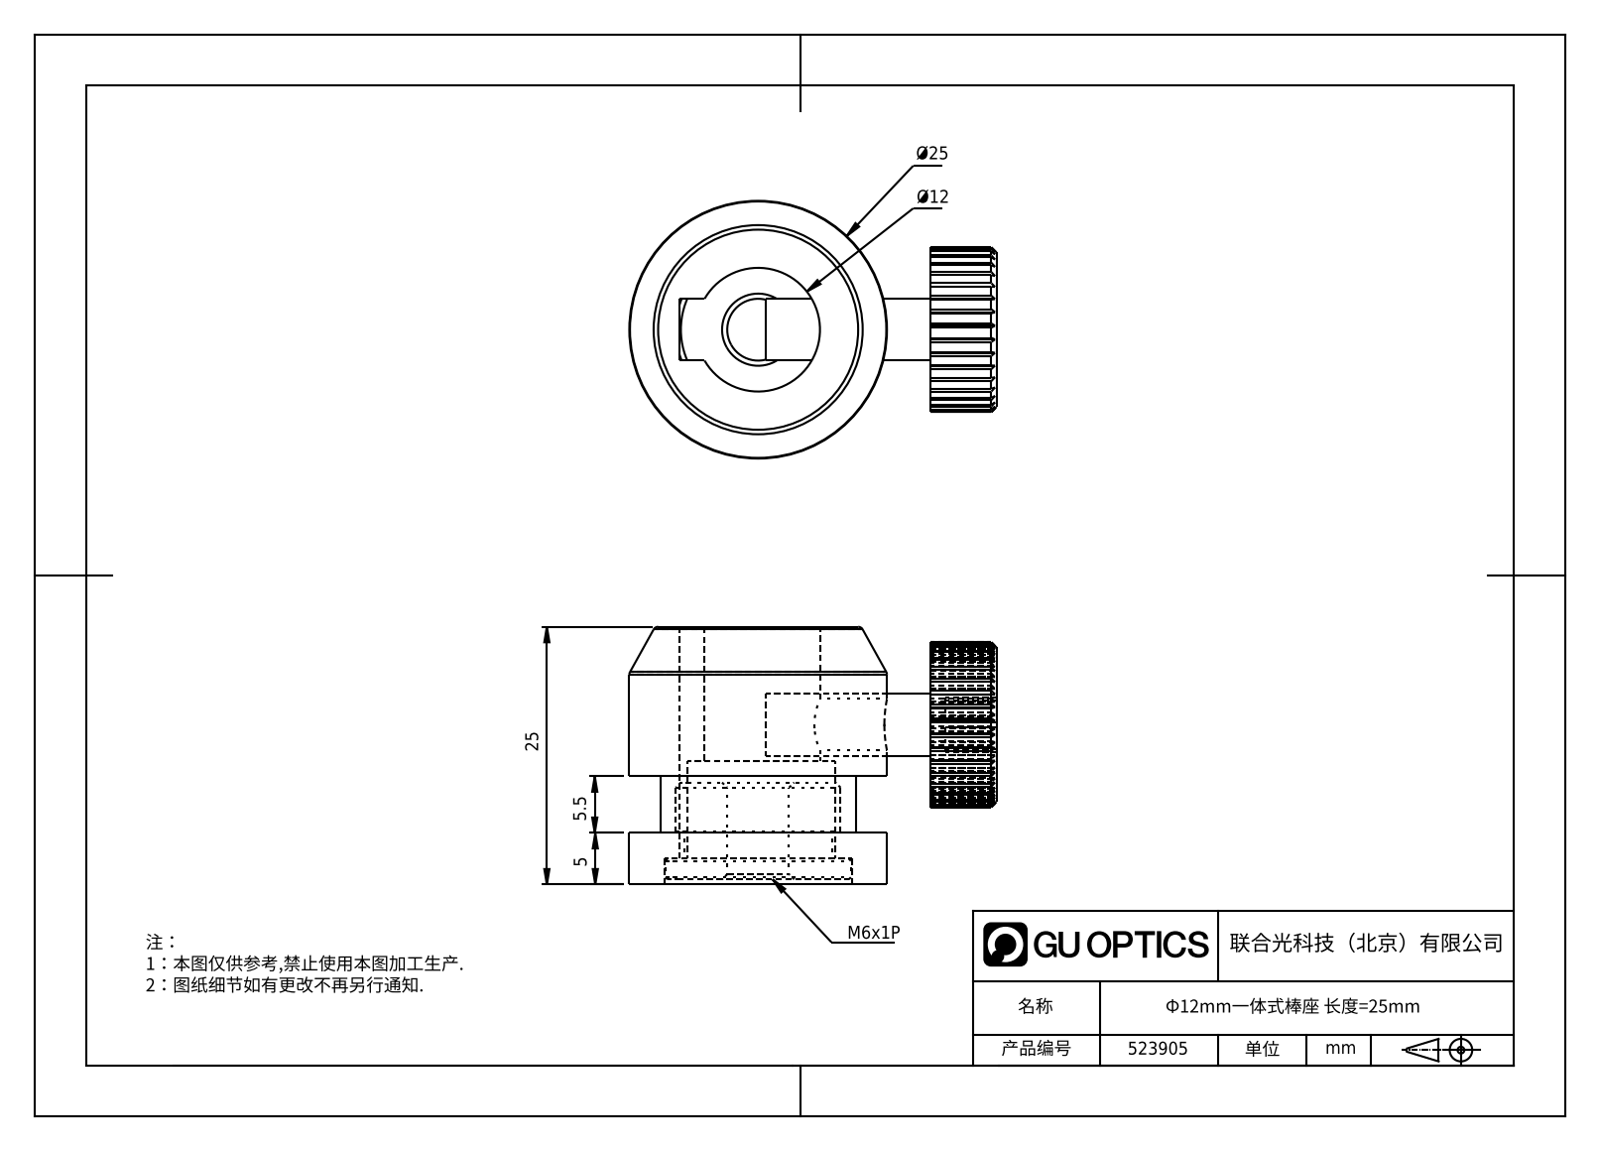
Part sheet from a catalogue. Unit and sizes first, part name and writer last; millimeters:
Units: millimetres
Overall size (bounding box): 35.63 × 25 × 25
Round holes (diameter × count): ⌀6 ×1, ⌀12 ×1, ⌀15 ×1, ⌀18.2 ×1
Round bosses / shafts (diameter × count): ⌀25 ×1, ⌀19 ×1, ⌀18 ×1, ⌀14.3 ×1, ⌀6 ×1
Partial cylindrical surfaces — rounded edges, fillets, slot ends (radius × count): R8 ×2
Main face-to-face distances: 5, 10.5, 5.5, 0.5, 4.5, 10, 25, 24.5, 20, 14.5
Volume: 9 683 mm³ · Surface area: 5 515 mm²
Bodies: 1 solid, 154 faces (95 planar, 50 cylindrical, 9 other)
Part name (STEP PRODUCT): 523905
STEP written by: SolidWorks 2020 (CONFIG_CONTROL_DESIGN)
